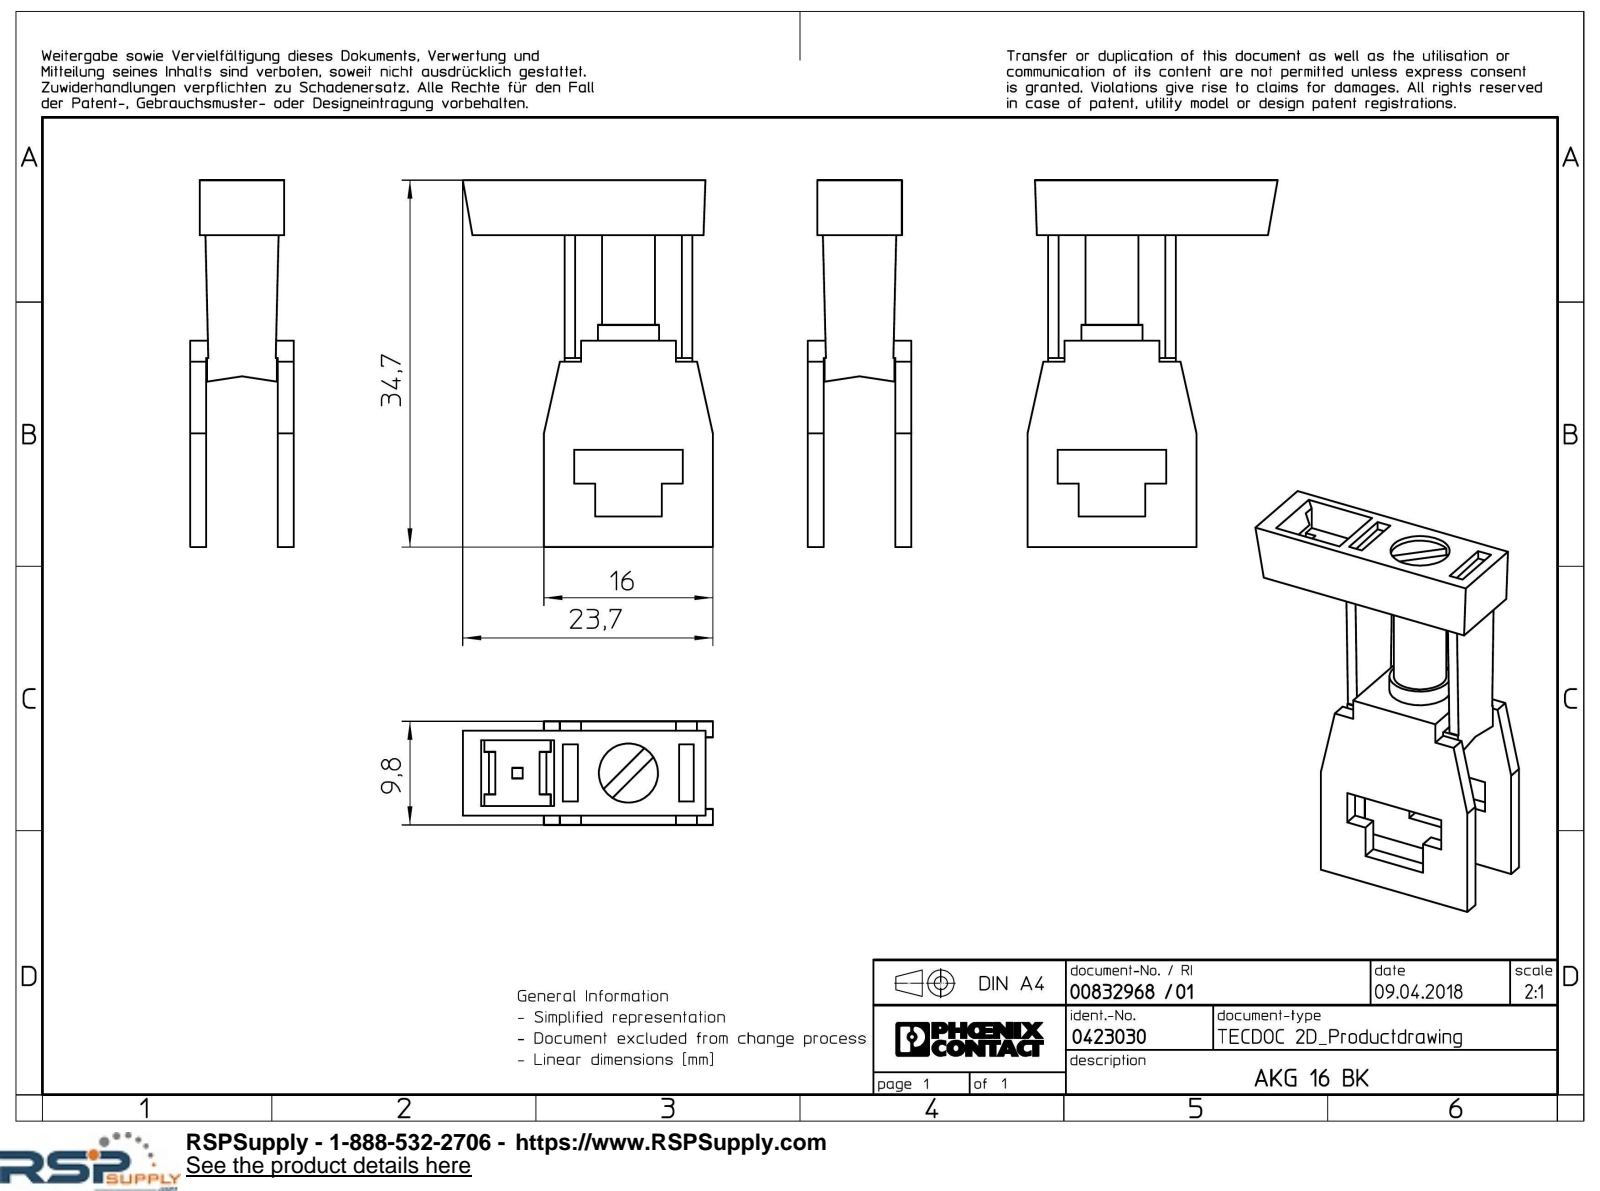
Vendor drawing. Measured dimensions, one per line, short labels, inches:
name: AKG_16_BK-select
written by: Creo Elements/Direct Modeling 20.1A 29-Sep-2018 (C) Parametric Technology GmbH (AUTOMOTIVE_DESIGN)
unit: in
bodies: 1 solid, 104 faces (98 planar, 6 cylindrical, 0 other)
size: 1.366 × 0.933 × 0.386
volume: 0.127 in³; area: 4.301 in²
holes: 1× ⌀0.22
bosses: 1× ⌀0.228, 1× ⌀0.197
face distances: 0.327, 0.059, 0.035, 0.024, 0.386, 0.35, 0.291, 0.268, 0.039, 0.315
